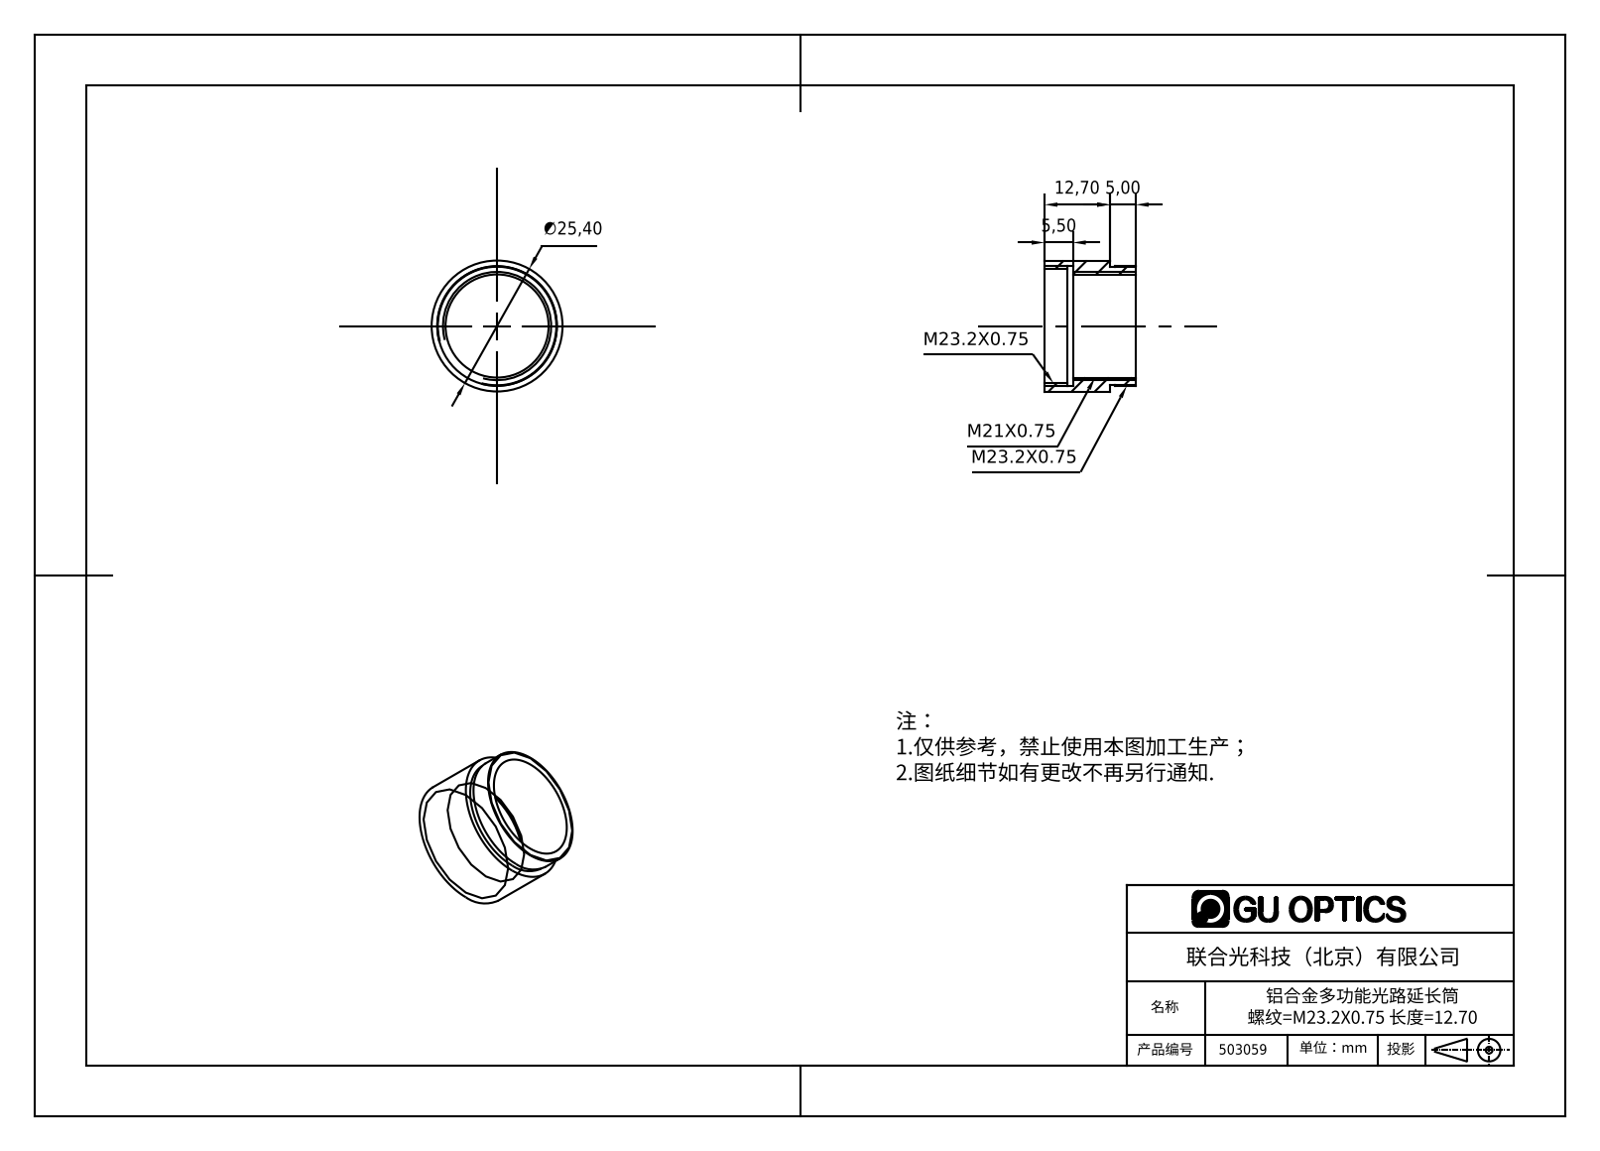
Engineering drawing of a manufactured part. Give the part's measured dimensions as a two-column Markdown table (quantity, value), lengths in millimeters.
| quantity | value |
| --- | --- |
| part name | 503059 |
| STEP written by | SolidWorks 2016 (AUTOMOTIVE_DESIGN) |
| units | millimeters |
| bodies | 1 solid, 18 faces (6 planar, 12 cylindrical, 0 other) |
| overall size | 25.4 × 25.4 × 17.7 |
| volume | 2 537 mm³ |
| surface area | 3 017 mm² |
| round holes (diameter × count) | 20 × 1, 22.2 × 1, 23.4 × 1 |
| round bosses / shafts (diameter × count) | 25.4 × 1, 23.2 × 1, 23 × 1 |
| main face-to-face distances | 5.5, 17.7, 12.2, 12.7, 7.2, 5, 1, 8.2, 4.5, 13.2 |
